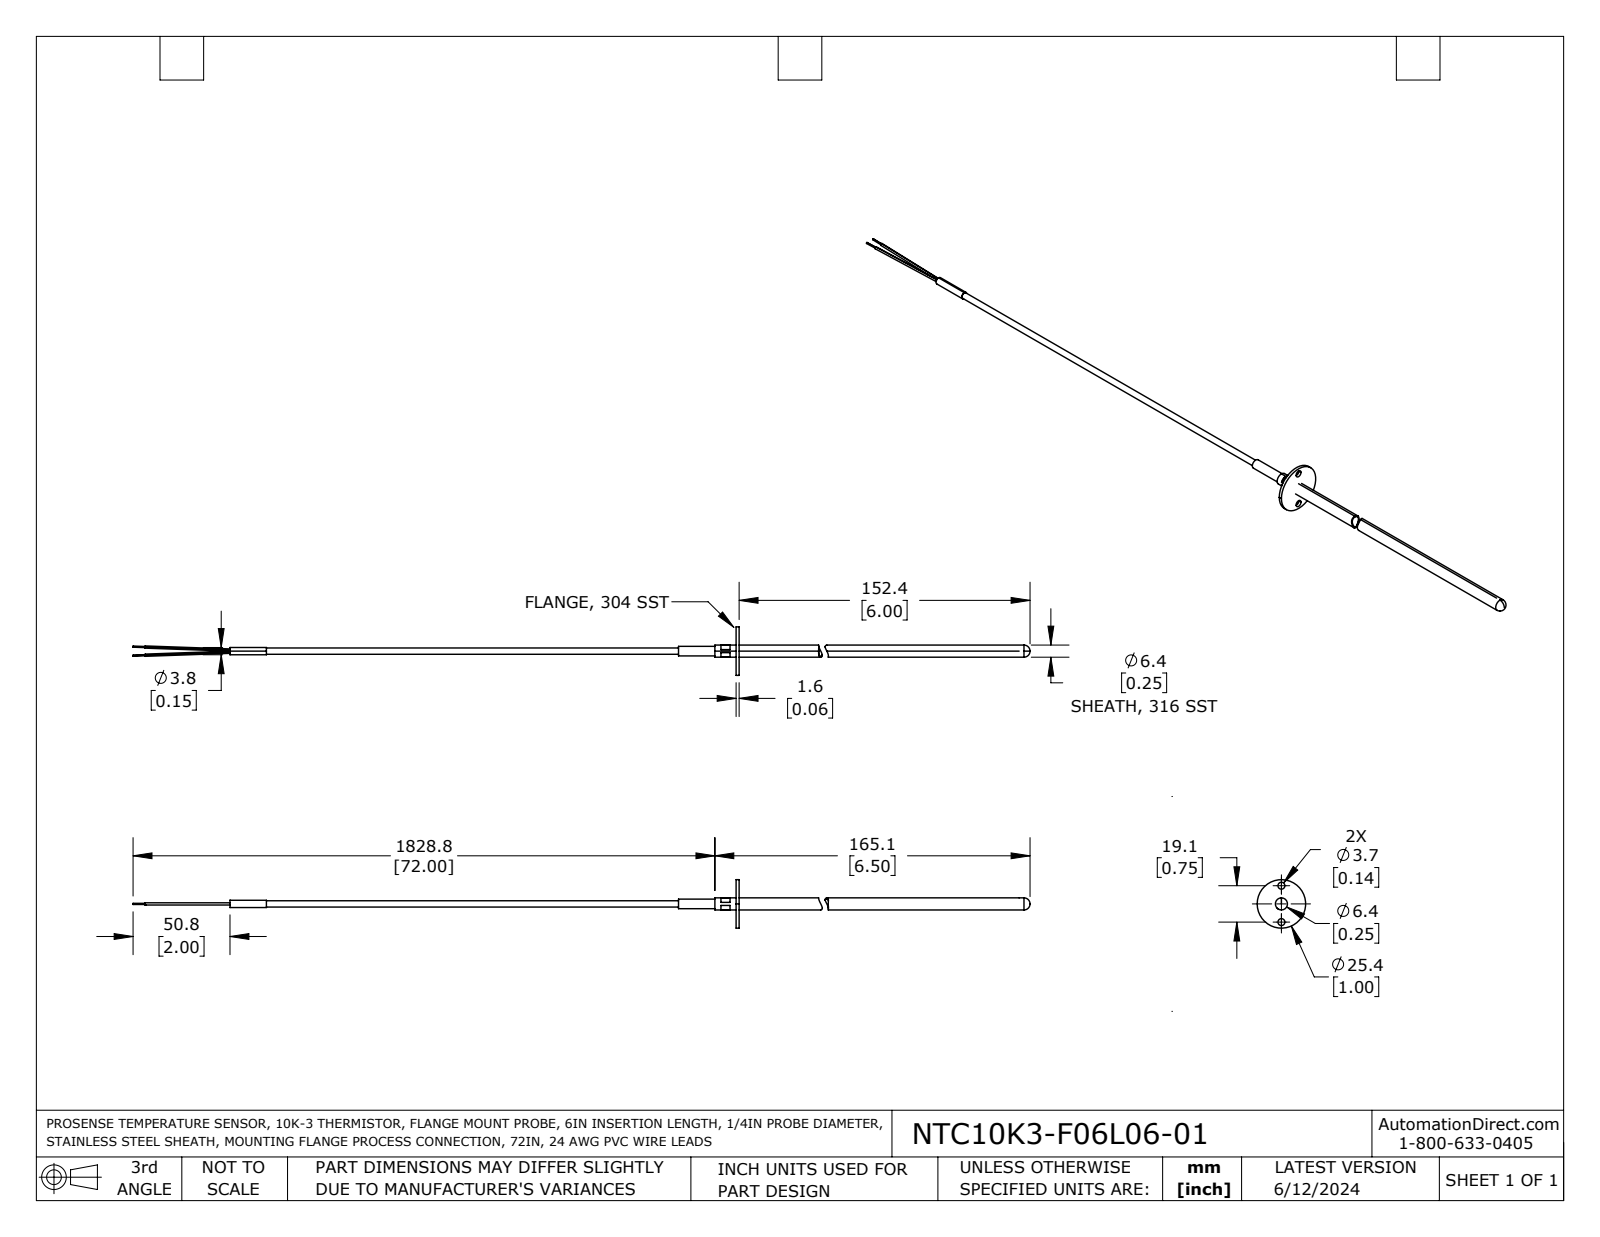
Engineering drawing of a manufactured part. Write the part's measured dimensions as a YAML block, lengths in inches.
part_name: "NTC10K3-F06L06-01"
step_written_by: "SolidWorks 2021 (AUTOMOTIVE_DESIGN)"
units: inches
bodies: {solids: 4, faces: 59, planar: 27, cylindrical: 22, other: 10}
overall_size: [18.495, 1, 1]
volume: 0.29
surface_area: 18.19
round_holes:
  - {diameter: 0.144, count: 2}
  - {diameter: 0.131, count: 1}
  - {diameter: 0.187, count: 1}
  - {diameter: 0.191, count: 1}
  - {diameter: 0.21, count: 1}
round_bosses_or_shafts:
  - {diameter: 1, count: 1}
  - {diameter: 0.25, count: 1}
  - {diameter: 0.197, count: 1}
  - {diameter: 0.15, count: 1}
  - {diameter: 0.13, count: 1}
face_to_face_distances: [0.063, 0.216, 5.837, 5.775, 0.437, 0.5, 6.275, 0.313, 10.001, 10.439]
hole_center_spacings: [0.375, 0.75]
